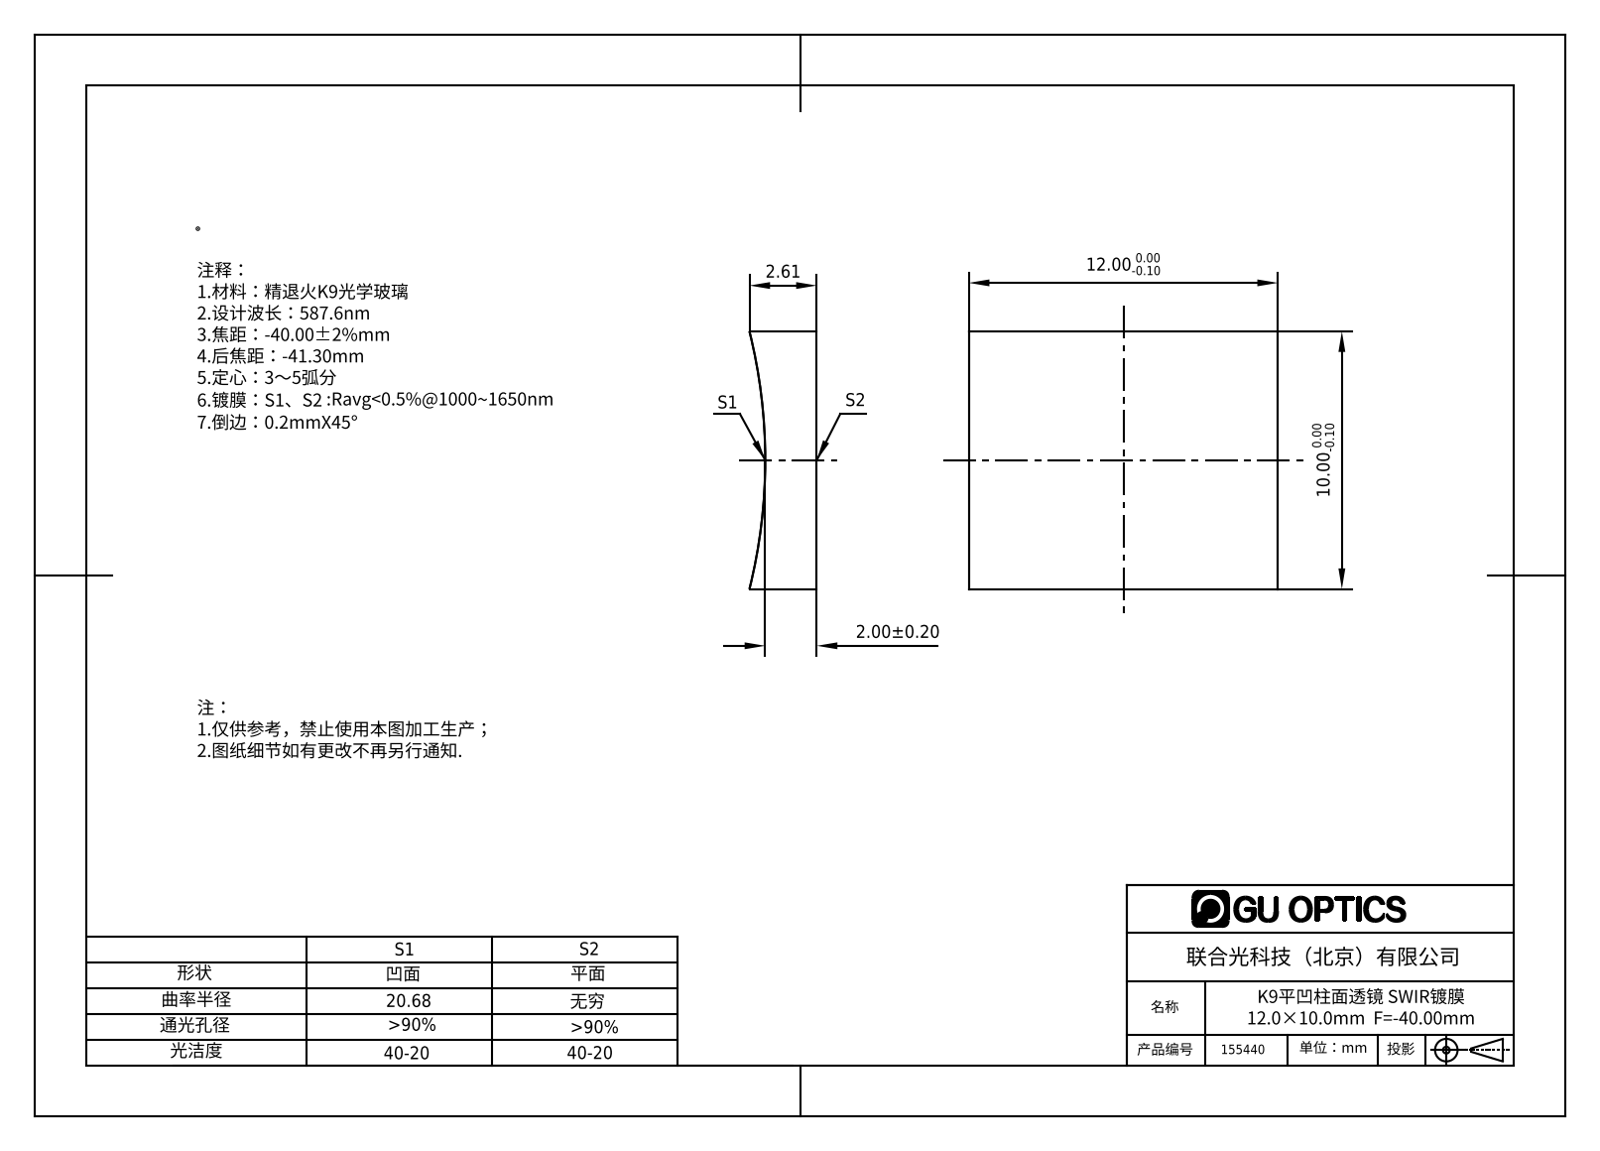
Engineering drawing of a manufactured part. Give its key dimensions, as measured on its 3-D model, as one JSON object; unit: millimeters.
{"part_name": "155341", "step_written_by": "SolidWorks 2016 (AUTOMOTIVE_DESIGN)", "units": "millimeters", "bodies": {"solids": 1, "faces": 6, "planar": 5, "cylindrical": 1, "other": 0}, "overall_size": [12, 10, 2.61], "volume_mm3": 264, "surface_area_mm2": 348, "partial_cylinders_radius": [[20.68, 1]], "face_to_face_distances": [10, 12]}
